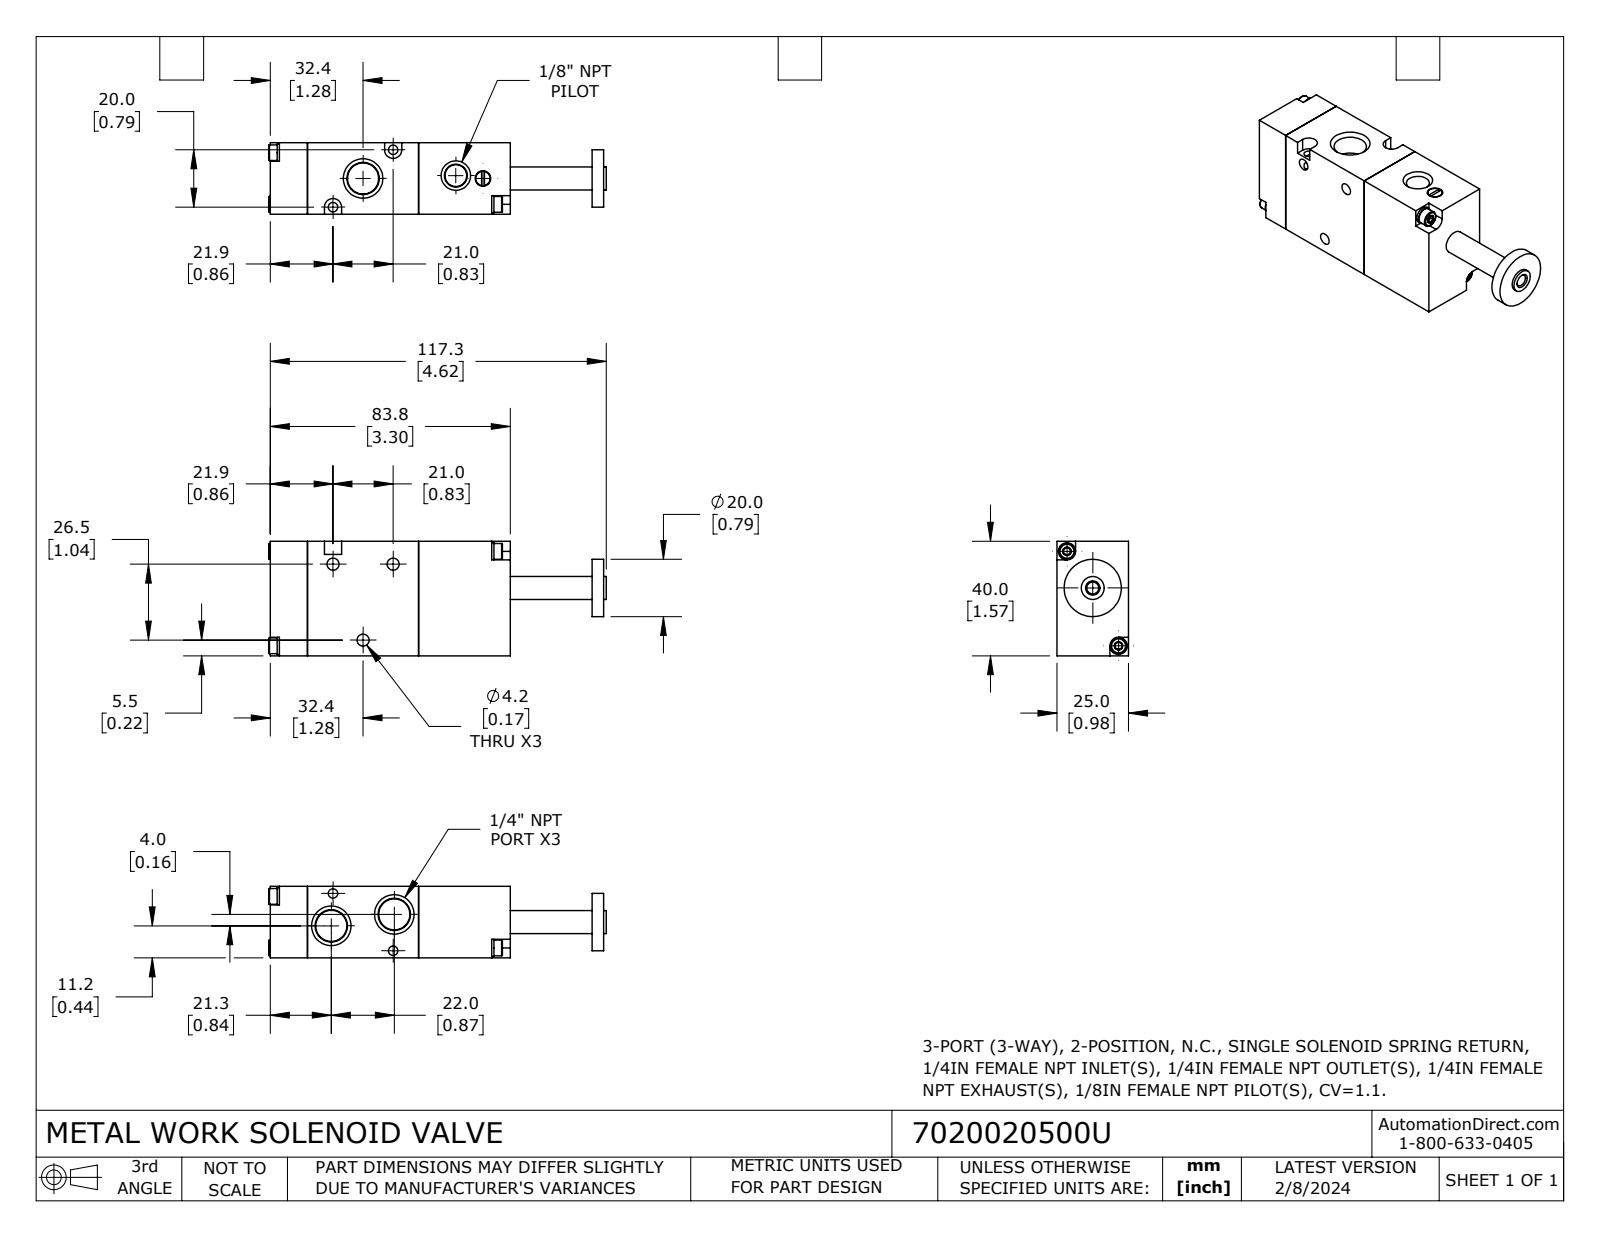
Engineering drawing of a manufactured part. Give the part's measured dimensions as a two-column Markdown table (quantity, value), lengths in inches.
| quantity | value |
| --- | --- |
| part name | 7020020500U |
| STEP written by | SolidWorks 2023 (CONFIG_CONTROL_DESIGN) |
| units | inches |
| bodies | 11 solids, 256 faces (117 planar, 65 cylindrical, 74 other) |
| overall size | 4.642 × 1.575 × 0.984 |
| volume | 4.986 in³ |
| surface area | 34.28 in² |
| round holes (diameter × count) | 0.118 × 4, 0.165 × 3, 0.13 × 2, 0.163 × 1, 0.213 × 1 |
| round bosses / shafts (diameter × count) | 0.236 × 4, 0.217 × 4, 0.787 × 1, 0.315 × 1, 0.197 × 1 |
| partial cylindrical surfaces (radius × count) | 0.118 × 2 |
| main face-to-face distances | 0.984, 1.528, 1.575, 0.512, 2.039, 3.299, 2.787, 1.26, 0.311, 1.264 |
| hole center spacings | 0.616, 0.709, 0.87, 1.122, 1.299, 1.48, 0.827, 1.142 |
